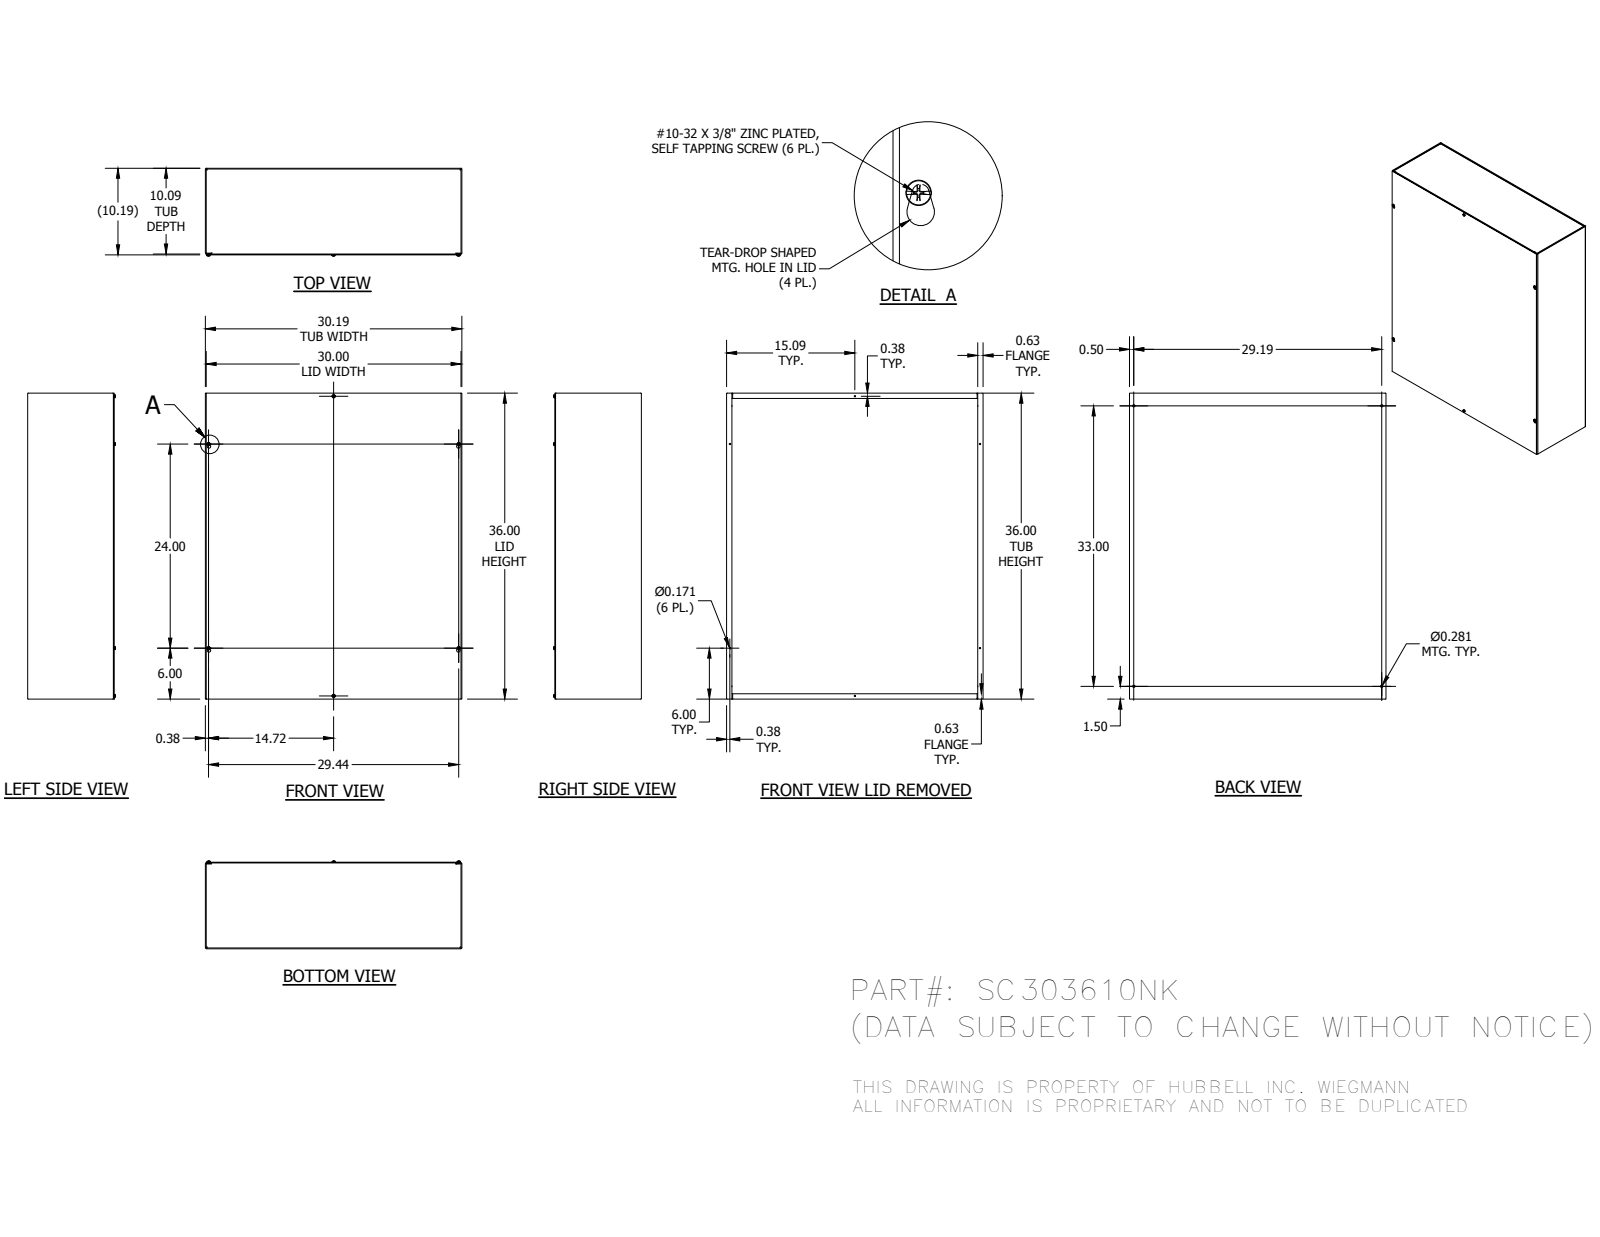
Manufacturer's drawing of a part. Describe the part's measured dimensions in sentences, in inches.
The part is named "SC303610NKBLR; SC3010NKTB; SC3036LPA; 37214 (+1 more)". Its 3-D file was written by "Autodesk Inventor 2014 (AUTOMOTIVE_DESIGN)". It is 10 solids with 404 faces: 232 planar, 50 cylindrical and 122 other. Overall it measures 36 by 30.187 by 10.319 inches. Its volume is 337.5 cubic inches and its surface area 7 246 square inches. Round holes: 6 of diameter 0.171, 4 of diameter 0.281, 2 of diameter 0.312. Round bosses or shafts: 6 of diameter 0.19. Partial cylindrical surfaces (rounded edges, fillets, slot ends): 12 of radius 0.016, 12 of radius 0.109, 4 of radius 0.125, 4 of radius 0.203. The main face-to-face distances are 0.094, 10.094, 10, 10.187, 30.094, 35.906, 30, 30.187, 36, 35.813. The hole center spacings are 4.502, 14.637, 15.757, 28.5, 29.656, 33.08, 37.115, 40.884.
